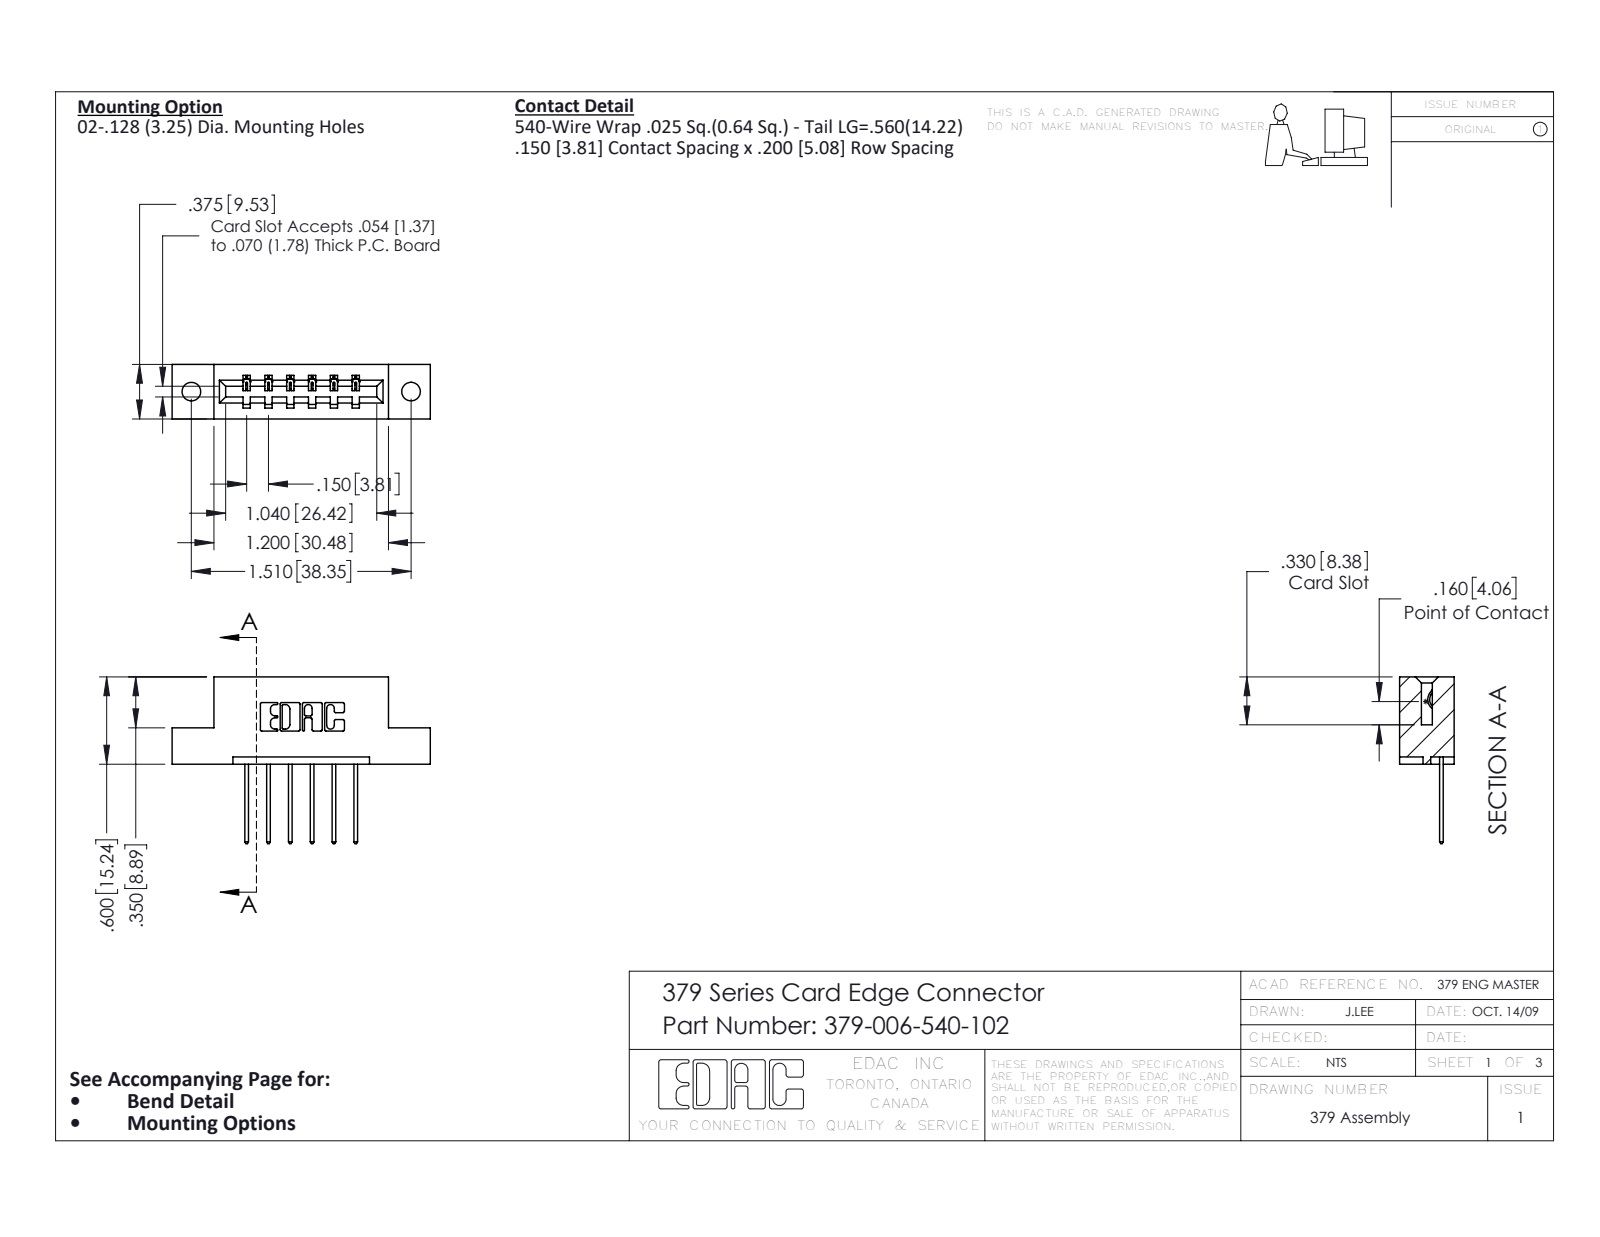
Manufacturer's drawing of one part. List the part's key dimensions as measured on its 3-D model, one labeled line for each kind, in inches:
Part name (STEP PRODUCT): 345-292-001_345-293-140; 379-006-540-102; 379 Part_Flush - .128 Dia
STEP written by: SolidWorks 2016 (CONFIG_CONTROL_DESIGN)
Units: inches
Bodies: 7 solids, 462 faces (322 planar, 140 cylindrical, 0 other)
Overall size (bounding box): 1.775 × 1.147 × 0.375
Volume: 0.261 in³ · Surface area: 6.184 in²
Round holes (diameter × count): ⌀0.128 ×2
Partial cylindrical surfaces — rounded edges, fillets, slot ends (radius × count): R0.01 ×22, R0.006 ×12, R0.01 ×12, R0.007 ×6, R0.031 ×6, R0.026 ×3, R0.014 ×1, R0.022 ×1
Main face-to-face distances: 0.3, 0.2, 0.375, 0.05, 0.15, 0.075, 0.1, 0.25, 0.35, 0.6
Hole centre spacings: 1.51
